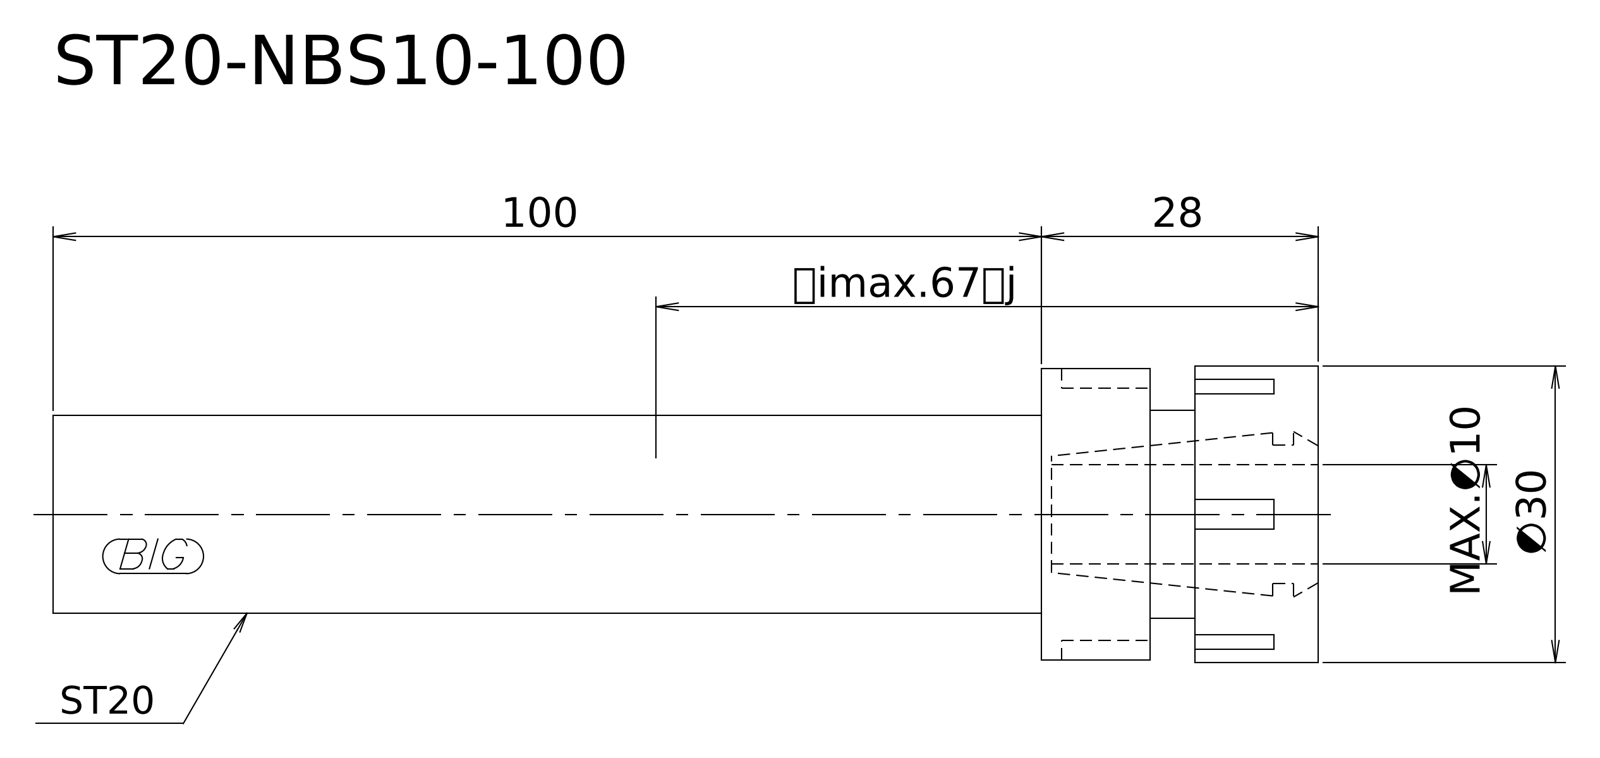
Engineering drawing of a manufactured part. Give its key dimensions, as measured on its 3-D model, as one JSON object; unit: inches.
{"step_written_by": "Kubotek KeyCreator V8.5.1 (14335) (CONFIG_CONTROL_DESIGN)", "units": "inches", "bodies": {"solids": 1, "faces": 9, "planar": 5, "cylindrical": 4, "other": 0}, "overall_size": [5.039, 1.181, 1.181], "volume_in3": 3.01, "surface_area_in2": 16.84, "round_bosses_or_shafts": [[1.181, 1], [1.161, 1], [0.827, 1], [0.787, 1]], "face_to_face_distances": [1.102, 0.492, 0.61, 0.669, 0.177, 0.433, 5.039, 4.547, 4.37, 3.937]}
